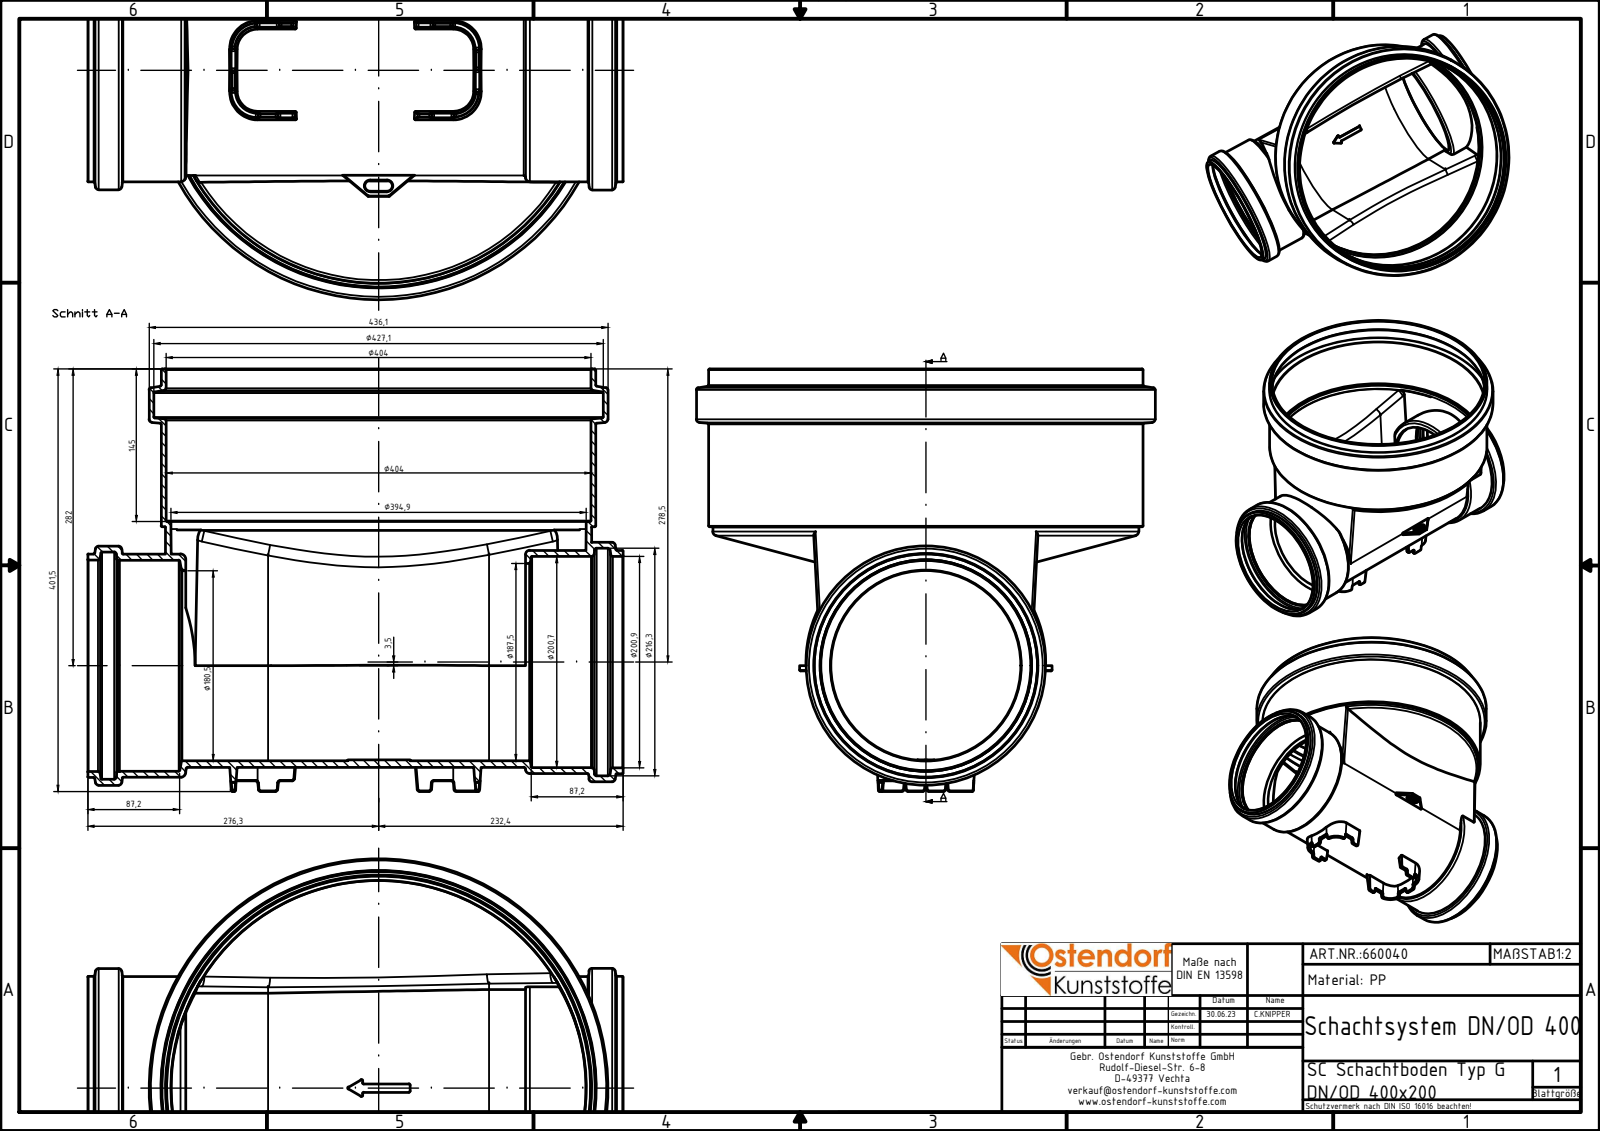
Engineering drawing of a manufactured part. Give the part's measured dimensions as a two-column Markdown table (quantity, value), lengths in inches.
| quantity | value |
| --- | --- |
| part name | 660040 |
| STEP written by | Autodesk Inventor 2020 (AUTOMOTIVE_DESIGN) |
| units | inches |
| bodies | 1 solid, 411 faces (84 planar, 131 cylindrical, 196 other) |
| overall size | 20.028 × 17.169 × 15.807 |
| volume | 216.9 in³ |
| surface area | 1 938 in² |
| round holes (diameter × count) | 7.909 × 2, 7.106 × 1, 7.382 × 1, 7.898 × 1, 7.902 × 1, 7.913 × 1, 8.501 × 1, 8.516 × 1, 15.906 × 1, 16.815 × 1 |
| round bosses / shafts (diameter × count) | 8.358 × 2, 17.169 × 1, 16.26 × 1, 15.941 × 1, 8.965 × 1, 8.95 × 1, 8.35 × 1, 8.346 × 1 |
| partial cylindrical surfaces (radius × count) | 0.039 × 54, 0.079 × 32, 0.043 × 7, 0.197 × 4, 3.939 × 1 |
| main face-to-face distances | 0.197, 3.379, 5.906, 5.709, 20.028, 5.394, 16.381, 3.647, 3.661, 12.719 |
| hole center spacings | 0.138 |
